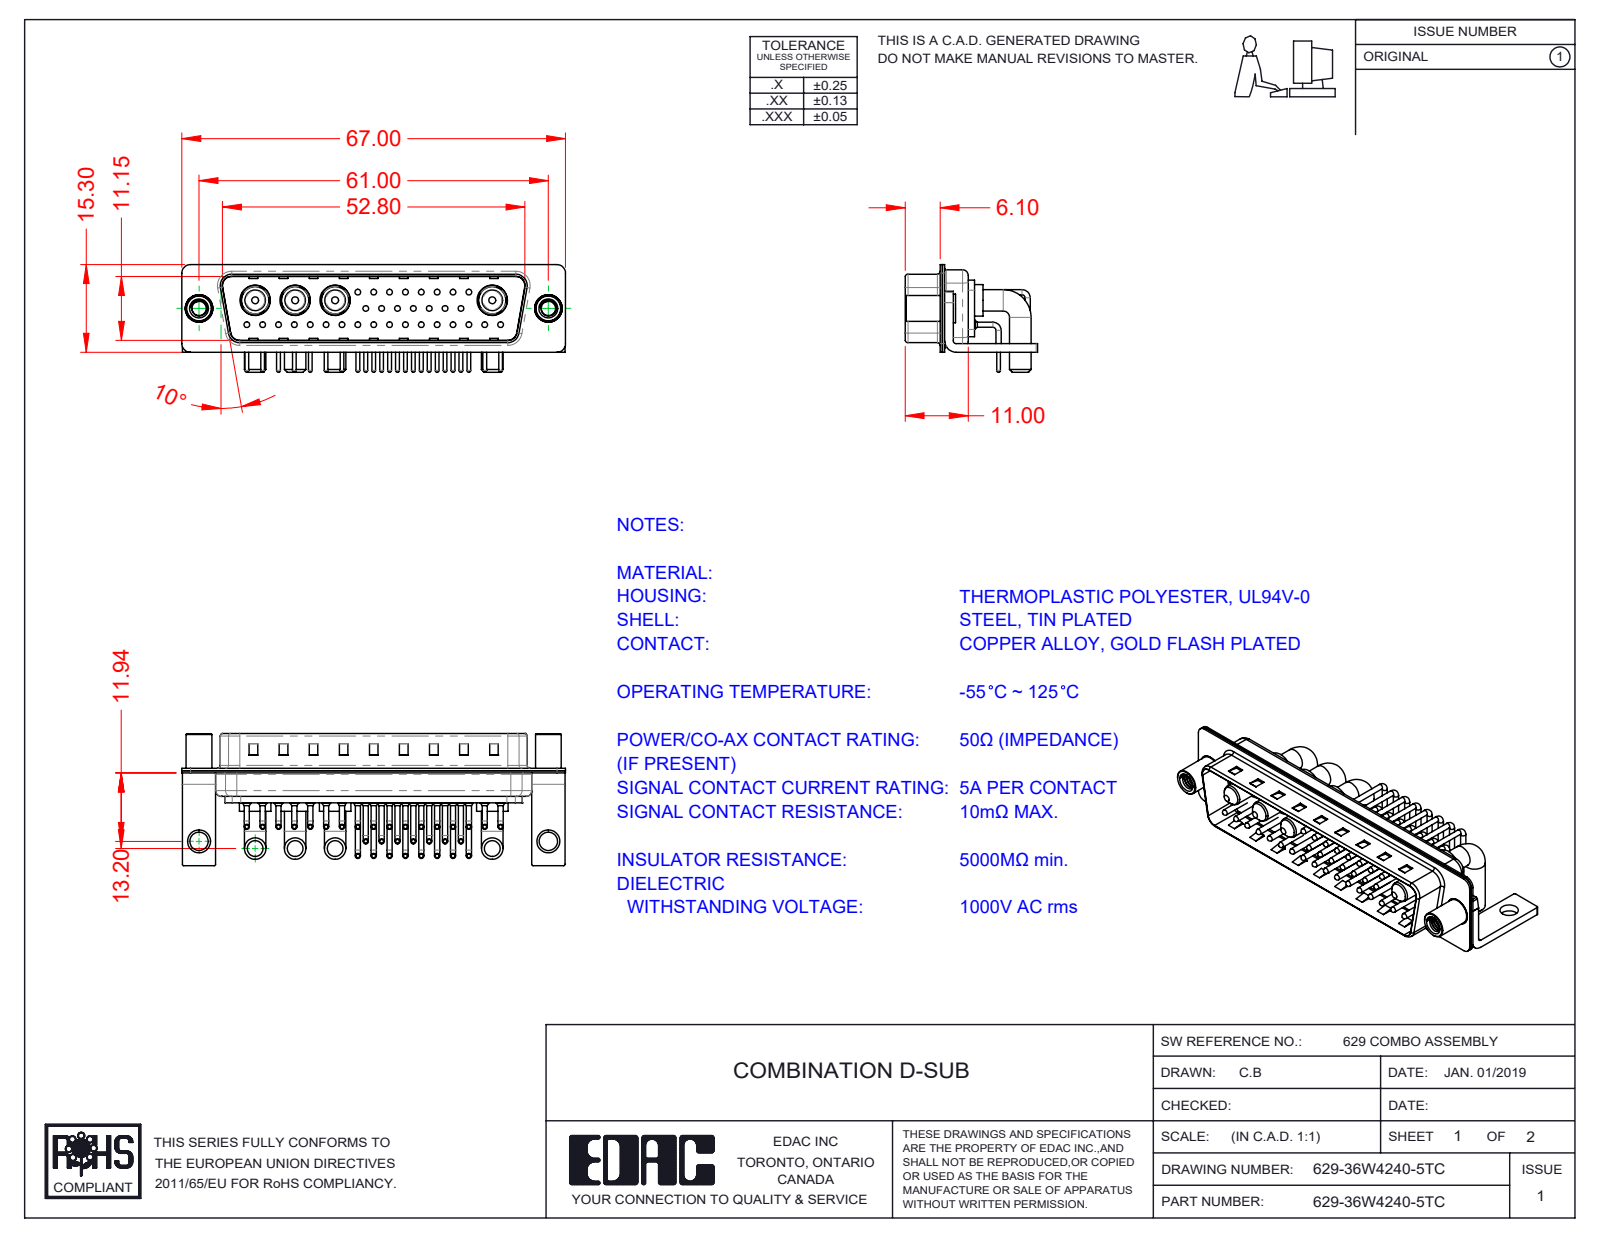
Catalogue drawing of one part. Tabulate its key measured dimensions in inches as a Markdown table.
| quantity | value |
| --- | --- |
| part name | 629Combo Stabilizer Bracket_50 Contacts; Power Pin_40A RA 50; 629Combo Contact Row 2_50 Contacts; 629Combo Threaded Standoff_D (+6 more) |
| STEP written by | SolidWorks 2020 (CONFIG_CONTROL_DESIGN) |
| units | inches |
| bodies | 47 solids, 4202 faces (2313 planar, 1449 cylindrical, 440 other) |
| overall size | 2.638 × 0.909 × 0.74 |
| volume | 0.38 in³ |
| surface area | 21.15 in² |
| round holes (diameter × count) | 0.03 × 32, 0.063 × 32, 0.079 × 32, 0.191 × 4, 0.209 × 4, 0.098 × 2, 0.126 × 2, 0.157 × 2, 0.189 × 2 |
| round bosses / shafts (diameter × count) | 0.035 × 64, 0.059 × 32, 0.039 × 32, 0.026 × 32, 0.148 × 8, 0.217 × 4, 0.205 × 4, 0.187 × 4 |
| partial cylindrical surfaces (radius × count) | 0.04 × 32, 0.01 × 16, 0.059 × 16, 0.079 × 13, 0.02 × 9, 0.063 × 8, 0.024 × 4, 0.026 × 4 |
| main face-to-face distances | 0.016, 0.059, 0.455, 0.22, 0.205, 0.031, 0.236, 0.031, 0.075, 0.043 |
| hole center spacings | 0.109, 0.218, 0.124, 0.327, 0.436, 0.545, 0.654, 0.763 |
